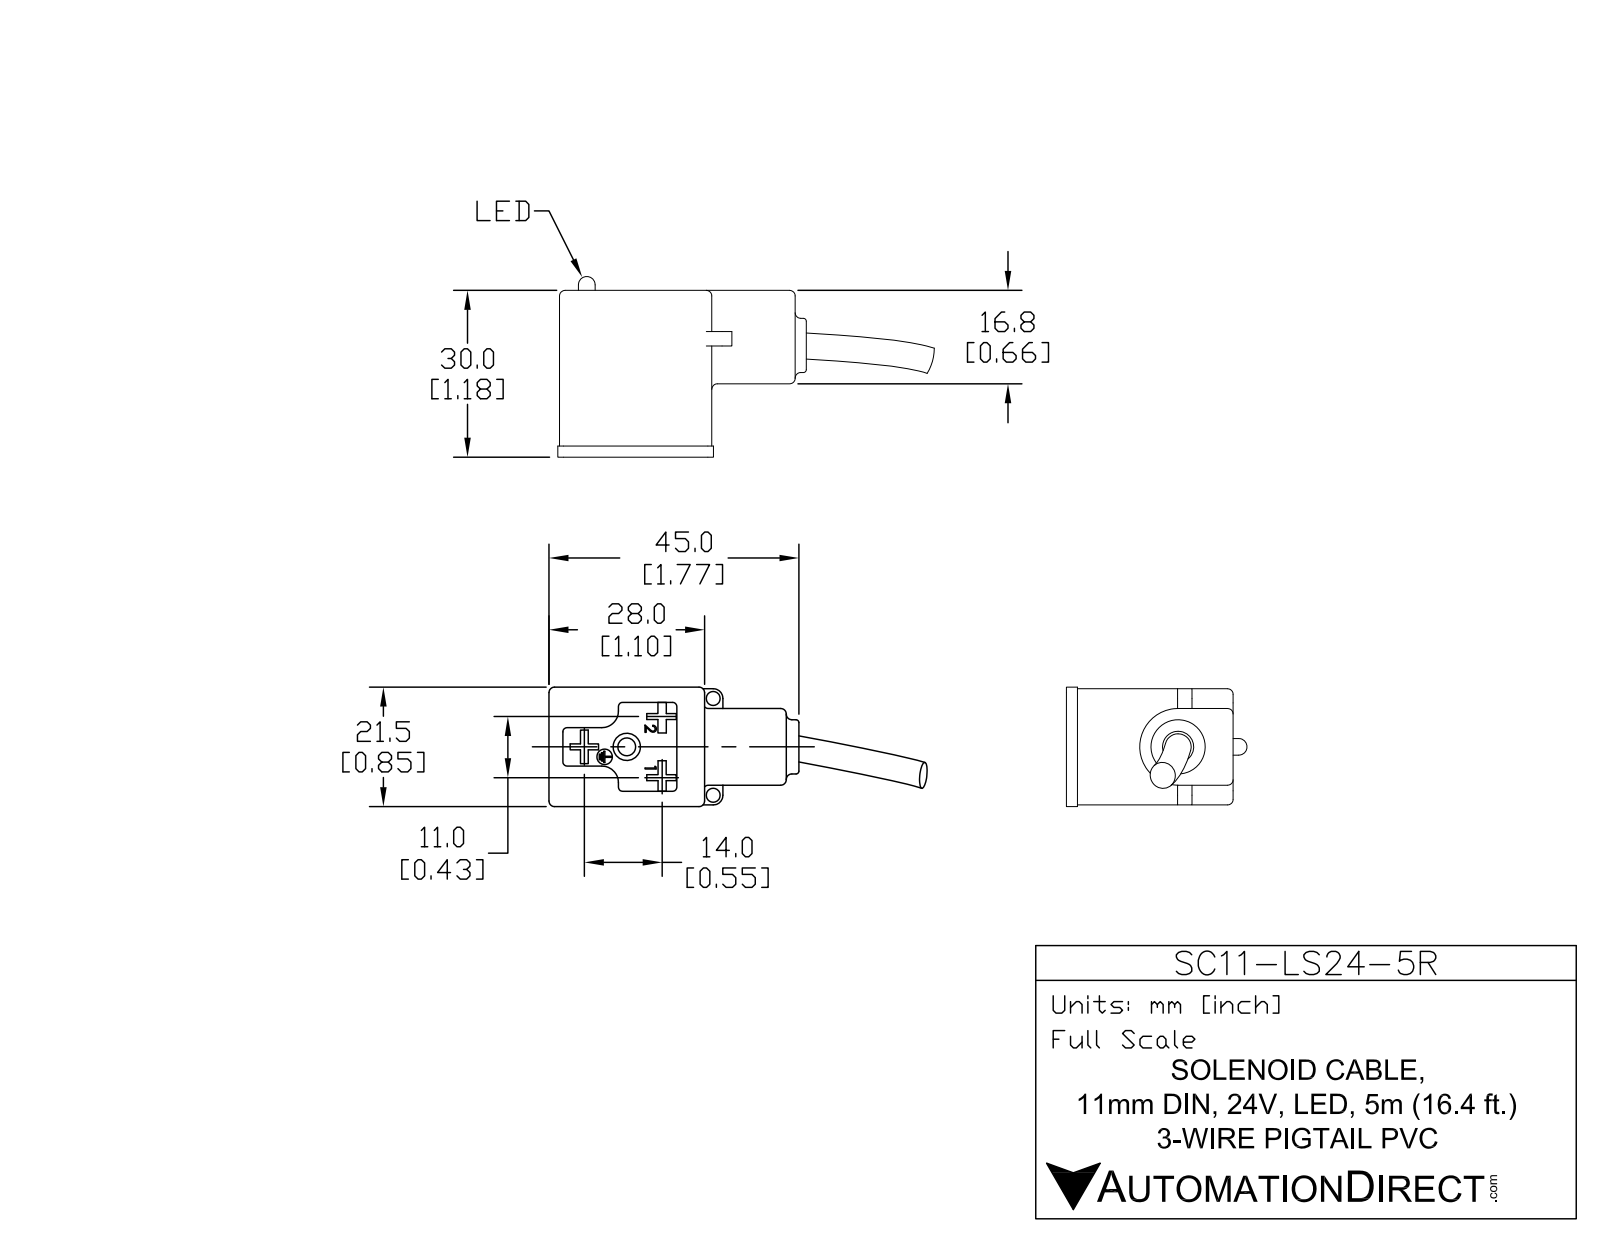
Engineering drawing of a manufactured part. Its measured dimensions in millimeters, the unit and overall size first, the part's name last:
Units: millimetres
Overall size (bounding box): 67.77 × 36.8 × 21.5
Round holes (diameter × count): ⌀2.5 ×2, ⌀2.78 ×1, ⌀3.2 ×1, ⌀4.9 ×1, ⌀5.6 ×1, ⌀6.6 ×1
Round bosses / shafts (diameter × count): ⌀9.75 ×1, ⌀6.5 ×1, ⌀3 ×1, ⌀2.75 ×1
Partial cylindrical surfaces — rounded edges, fillets, slot ends (radius × count): R0.75 ×21, R1 ×6, R1.75 ×2, R3 ×2, R6.9 ×1
Main face-to-face distances: 20.9, 2, 28, 30, 27.4, 3.55, 17.35, 7, 9.45, 27.95
Hole centre spacings: 17.82, 21.65, 4.27, 17.4
Volume: 19 939 mm³ · Surface area: 7 624 mm²
Bodies: 4 solids, 200 faces (132 planar, 46 cylindrical, 22 other)
Part name (STEP PRODUCT): SC11-LS24-5R
STEP written by: SolidWorks 2011 (AUTOMOTIVE_DESIGN)
